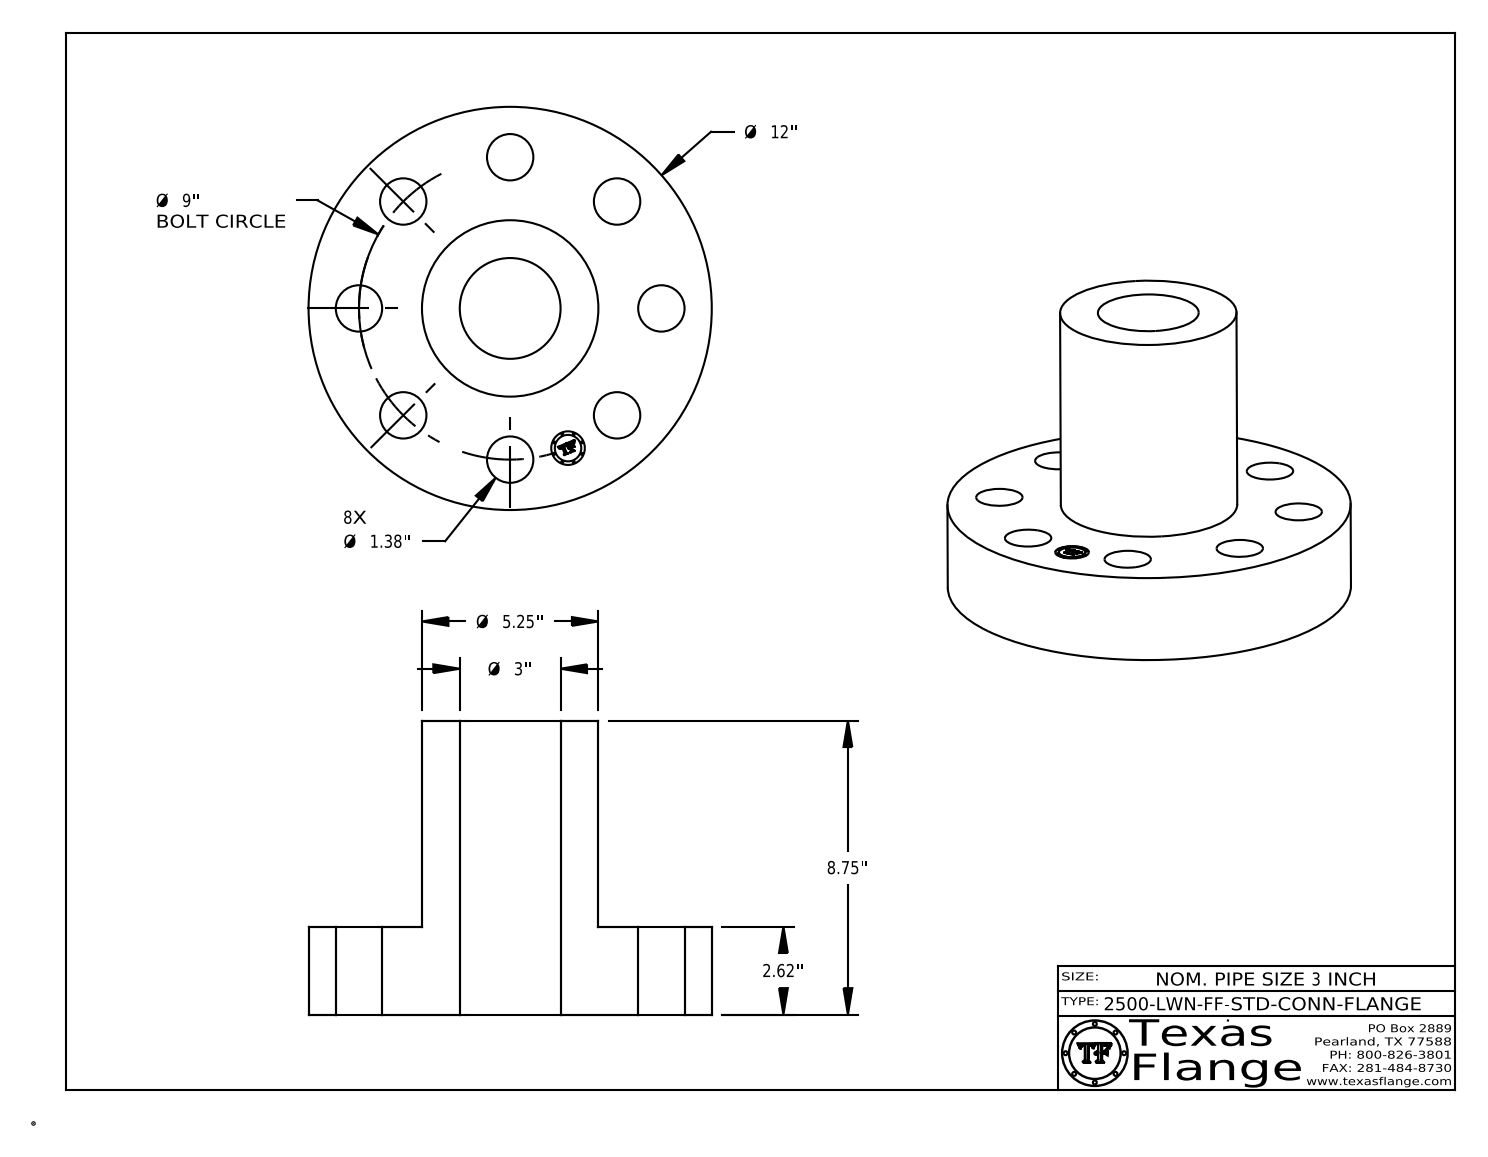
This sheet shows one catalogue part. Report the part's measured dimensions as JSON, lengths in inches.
{"part_name": "3-2500-LWN-FF-STD-CONN-FLANGE", "step_written_by": "CATIA V5 STEP AP214 (AUTOMOTIVE_DESIGN)", "units": "inches", "bodies": {"solids": 1, "faces": 410, "planar": 368, "cylindrical": 42, "other": 0}, "overall_size": [12, 12, 8.75], "volume_in3": 335.8, "surface_area_in2": 561.4, "round_holes": [[1.38, 8], [1, 1], [3, 1]], "round_bosses_or_shafts": [[0.061, 8], [12, 1], [5.25, 1], [0.788, 1]], "face_to_face_distances": [2.62, 8.75, 6.13, 2.615, 6.135, 0.298, 0.292, 0.019, 0.054, 0.194], "hole_center_spacings": [4.5, 3.444, 6.364, 8.315, 1.756, 5, 7.483, 9]}
